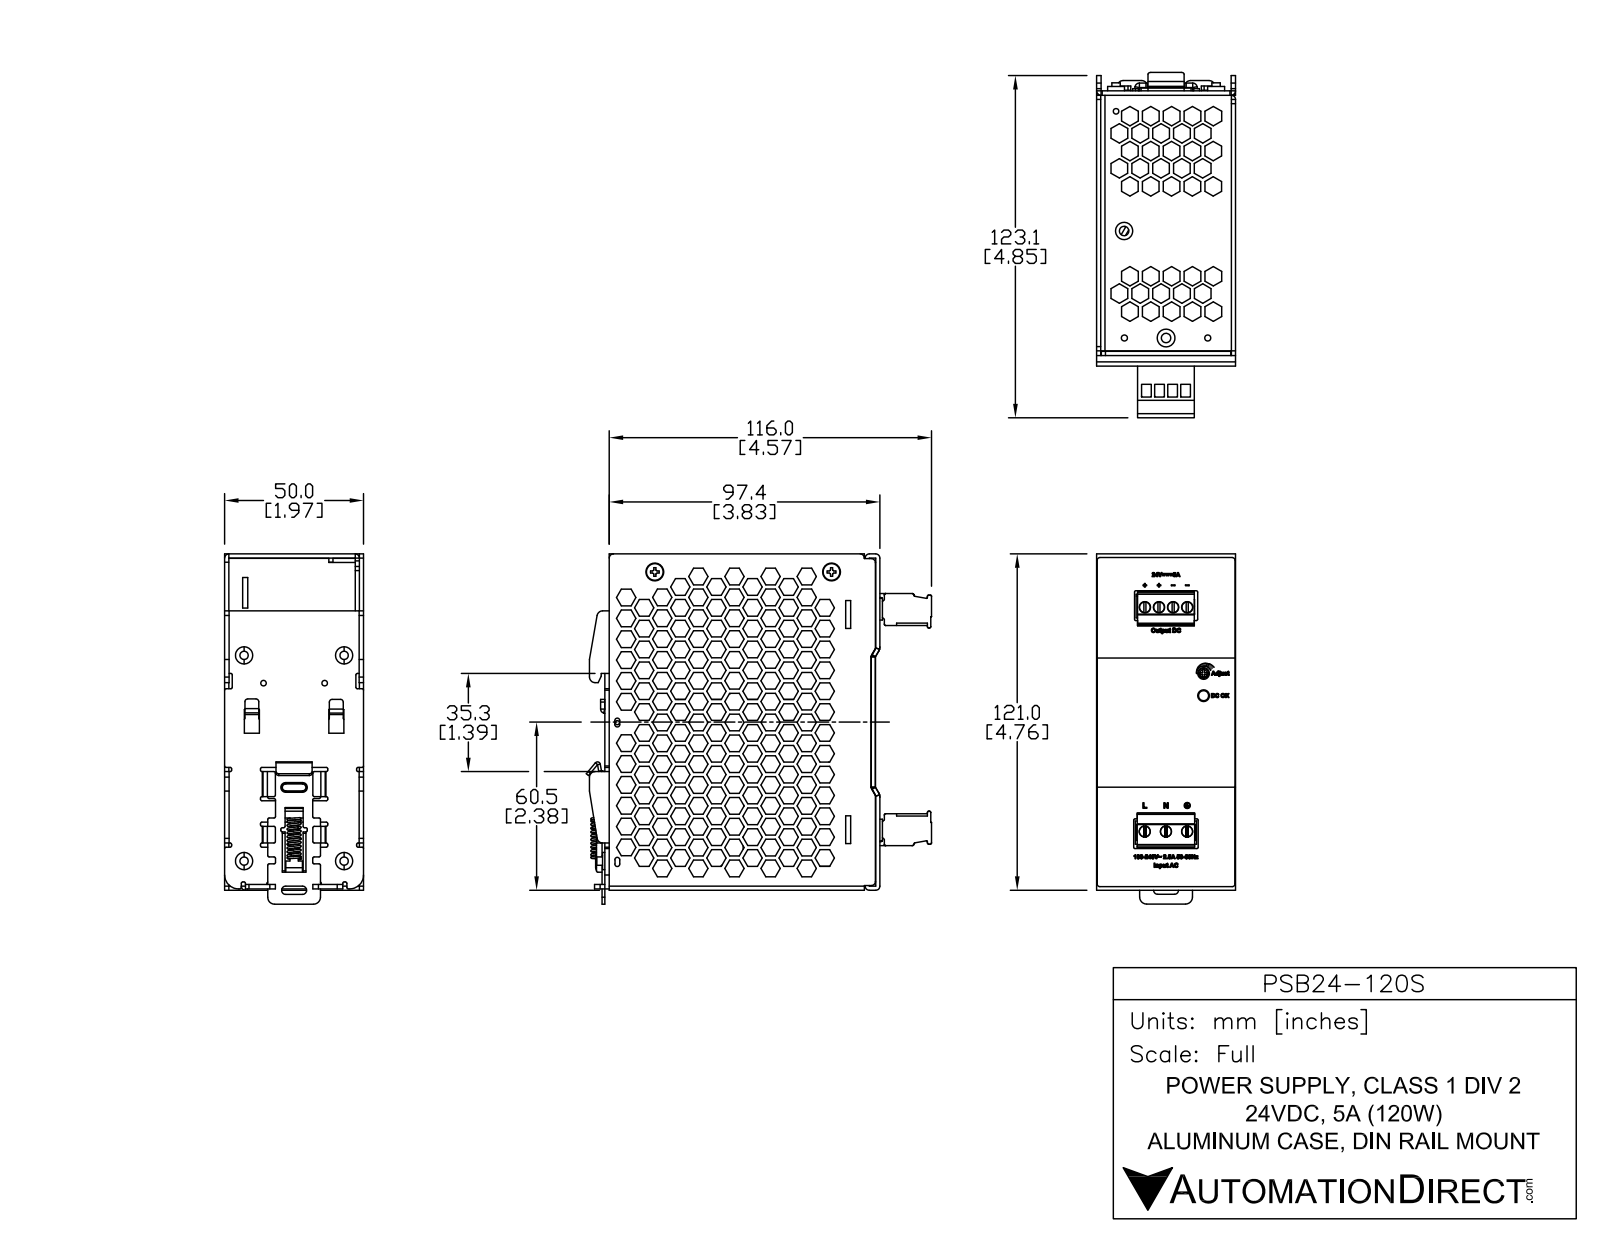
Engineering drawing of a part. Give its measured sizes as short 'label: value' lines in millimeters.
name: 3460088100_2; 331610470101; 3461303000_2; 3202315200_2 (+8 more)
written by: SolidWorks 2014 (AUTOMOTIVE_DESIGN)
unit: mm
bodies: 30 solids, 5579 faces (3833 planar, 707 cylindrical, 1039 other)
size: 126.05 × 124.94 × 50.1
volume: 98 816 mm³; area: 159 607 mm²
holes: 8× ⌀2.5, 7× ⌀4.05, 6× ⌀3, 4× ⌀3.5, 3× ⌀2, 3× ⌀4.2, 2× ⌀0.2, 2× ⌀2.2, 2× ⌀2.6, 2× ⌀3.6, 2× ⌀4, 1× ⌀2.26
bosses: 8× ⌀2.5, 7× ⌀3.95, 5× ⌀3, 4× ⌀5.5, 4× ⌀5.2, 4× ⌀4, 4× ⌀2.7, 3× ⌀5.6
rounds: 134× R0.5, 32× R1.5, 25× R1, 20× R0.1, 20× R0.4, 16× R0.15, 14× R2, 12× R0.3
face distances: 1.5, 1.6, 48.5, 6.5, 8.1, 96.5, 5, 6.6, 98, 11
hole spacings: 15, 30, 5.08, 7.62, 10.16, 12.21, 15.24, 15.28
